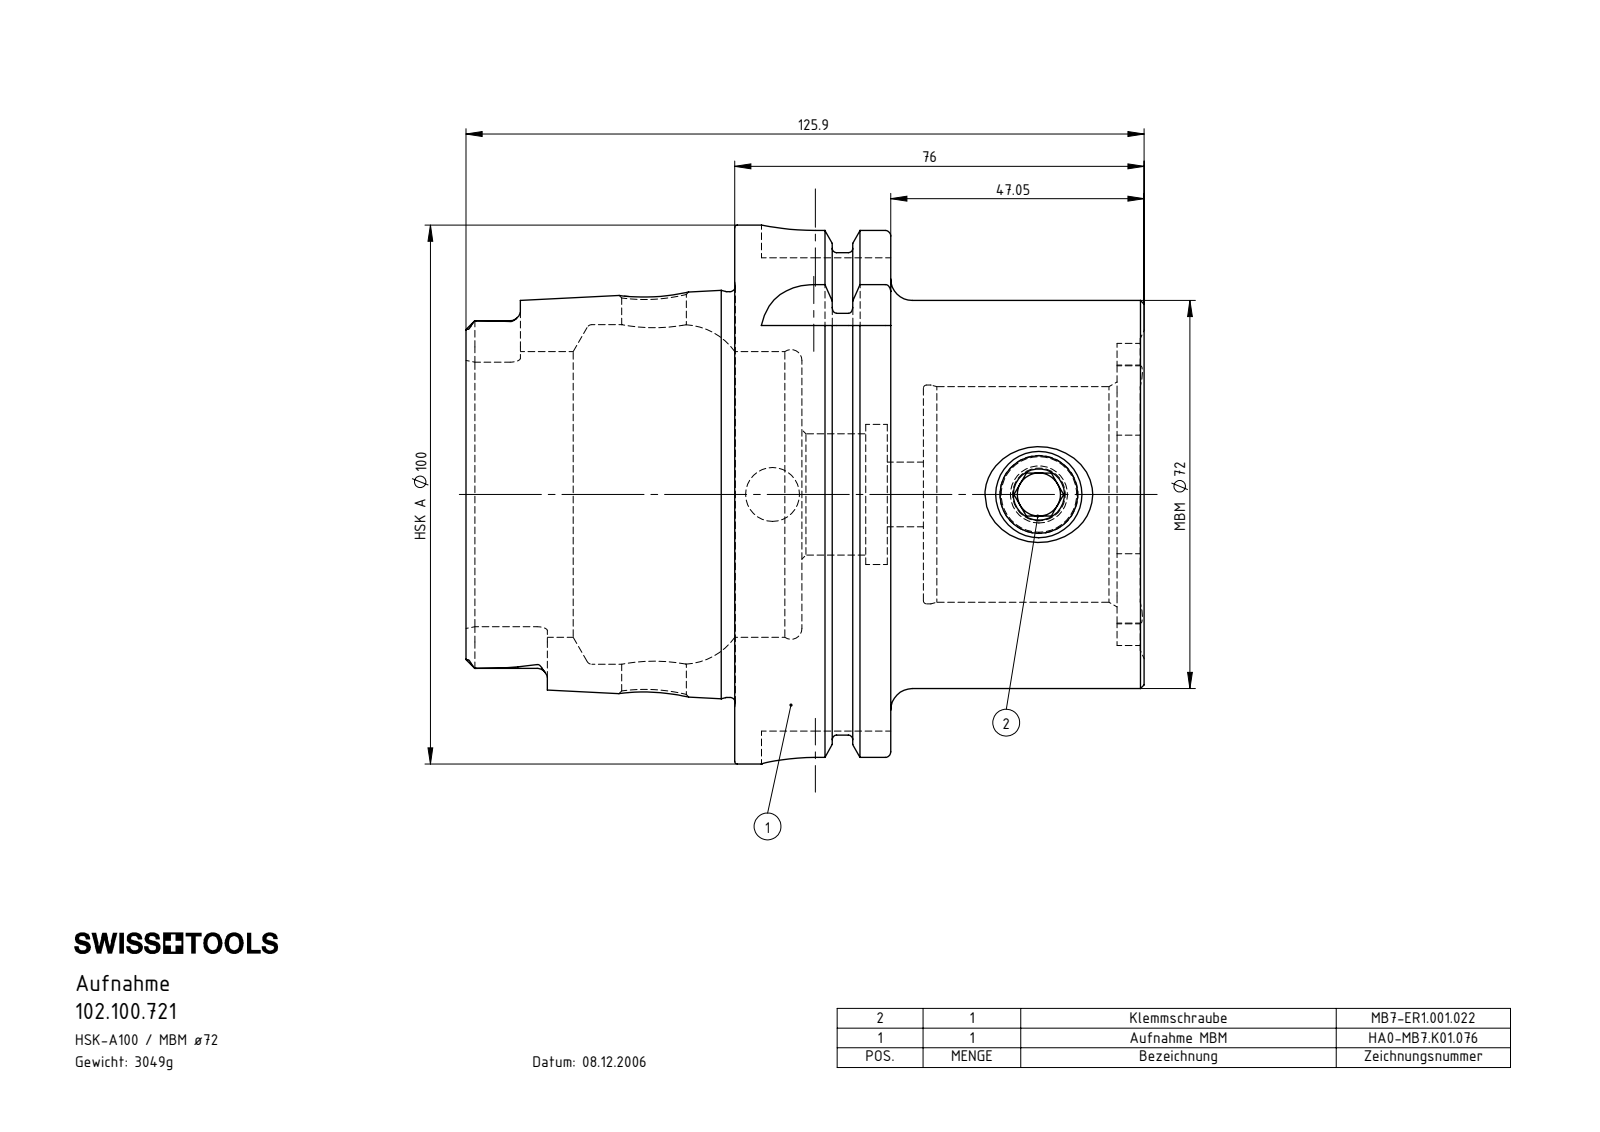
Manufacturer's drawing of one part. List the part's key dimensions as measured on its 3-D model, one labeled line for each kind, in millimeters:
Part name (STEP PRODUCT): HA0.MB7.K01.076; HA0-MB7.K01.076_A_Fertigbearbeitung; MB7-ER1.001.022_A
STEP written by: SolidWorks 2011 (CONFIG_CONTROL_DESIGN)
Units: millimetres
Bodies: 2 solids, 208 faces (58 planar, 65 cylindrical, 85 other)
Overall size (bounding box): 125.9 × 100 × 100
Volume: 388 571 mm³ · Surface area: 67 029 mm²
Round holes (diameter × count): ⌀12 ×2, ⌀10 ×1, ⌀14.5 ×1, ⌀22.5 ×1, ⌀26 ×1, ⌀40 ×1, ⌀40.6 ×1, ⌀53 ×1, ⌀63 ×1
Round bosses / shafts (diameter × count): ⌀100 ×1, ⌀91.95 ×1, ⌀75.26 ×1, ⌀72 ×1, ⌀16 ×1
Partial cylindrical surfaces — rounded edges, fillets, slot ends (radius × count): R1.9 ×6, R4.88 ×4, R5.2 ×4, R10 ×4, R23.75 ×1, R28.02 ×1
Main face-to-face distances: 28.95, 12.45, 16.5, 35, 22.55, 6.05, 76, 63.55, 47.05, 41
Hole centre spacings: 49.45
